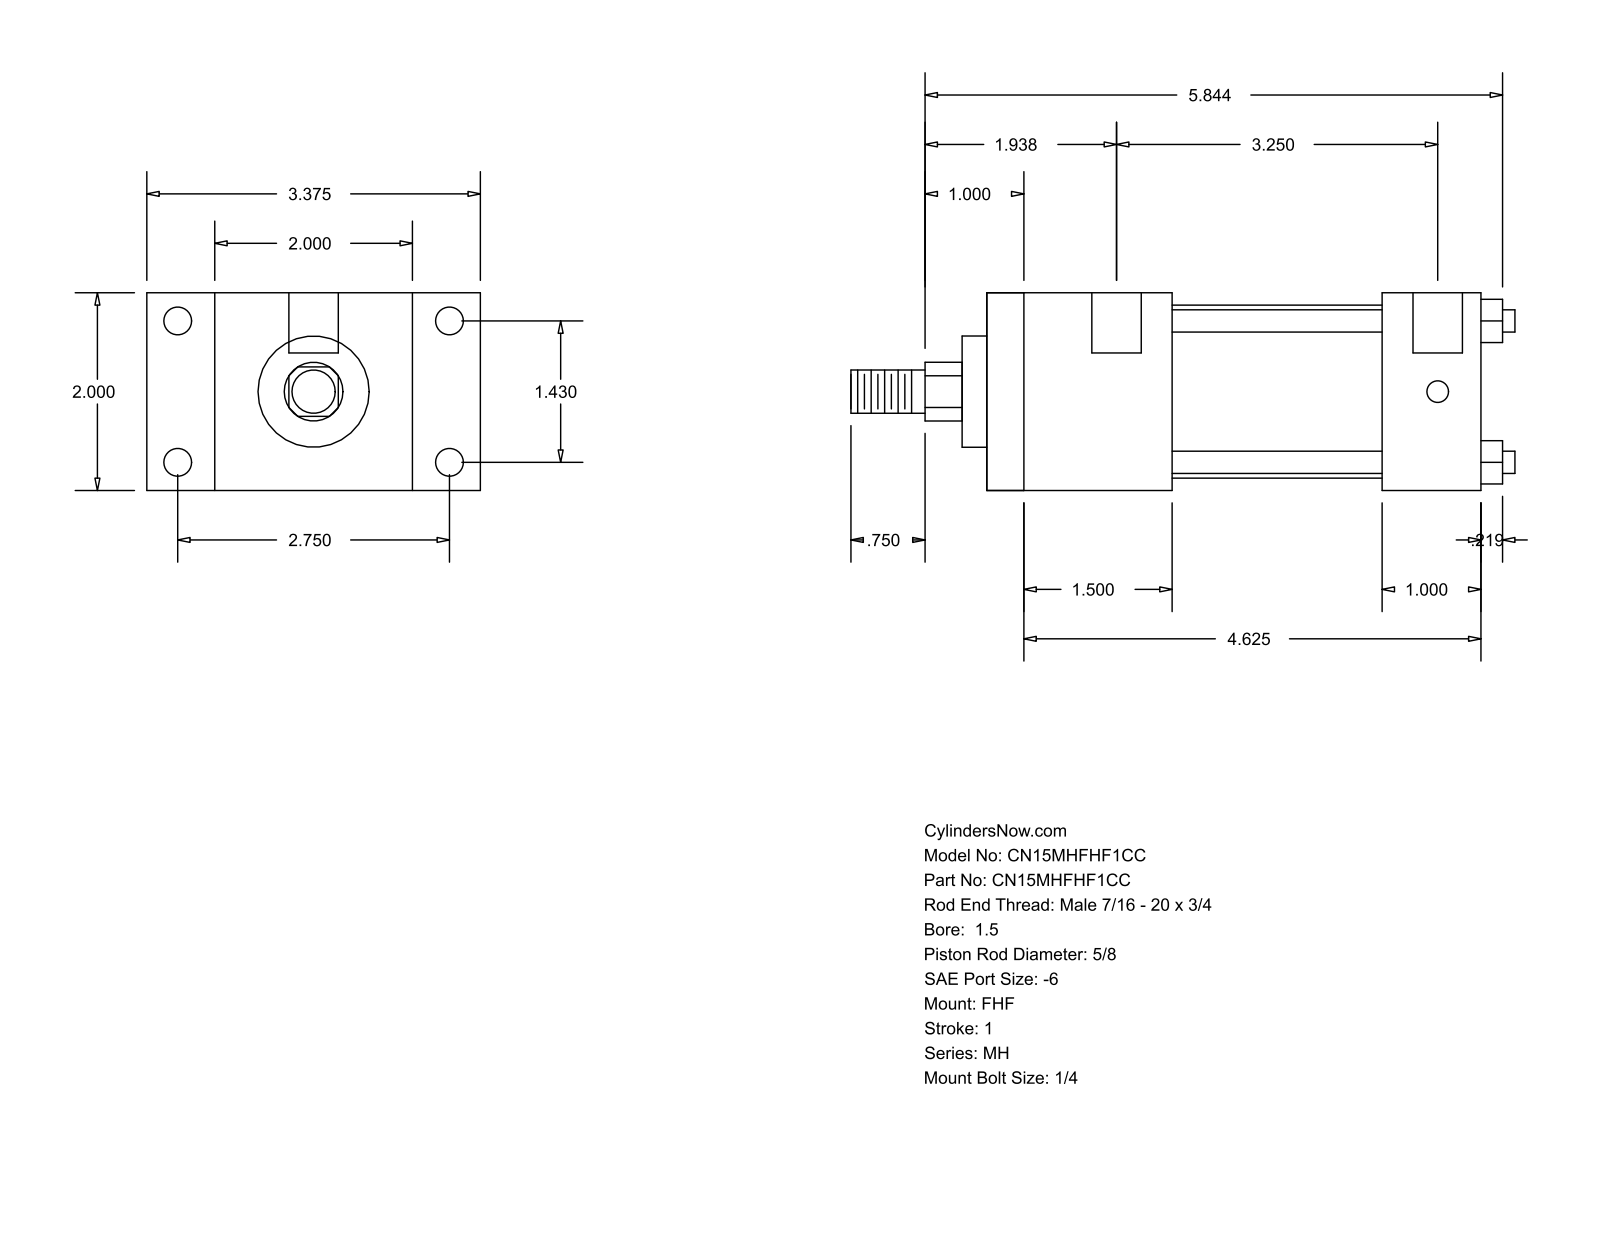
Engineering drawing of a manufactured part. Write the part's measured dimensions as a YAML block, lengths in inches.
part_name: "MH_FHF__0150_0.625"
step_written_by: "GSSL Pune (CONFIG_CONTROL_DESIGN)"
units: inches
bodies: {solids: 0, faces: 88, planar: 60, cylindrical: 28, other: 0}
overall_size: [6.719, 3.375, 2]
round_holes:
  - {diameter: 0.219, count: 4}
  - {diameter: 0.281, count: 4}
  - {diameter: 0.5, count: 2}
round_bosses_or_shafts:
  - {diameter: 0.225, count: 4}
  - {diameter: 1.75, count: 1}
  - {diameter: 1.125, count: 1}
  - {diameter: 0.625, count: 1}
  - {diameter: 0.437, count: 1}
partial_cylinders:
  - {radius: 0.297, count: 1}
face_to_face_distances: [2, 0.687, 2.687, 1.875, 3.375, 5, 3.125, 2.125, 4, 1]
hole_center_spacings: [1.43, 2.75, 3.099, 3.375, 0.125, 3.25]
